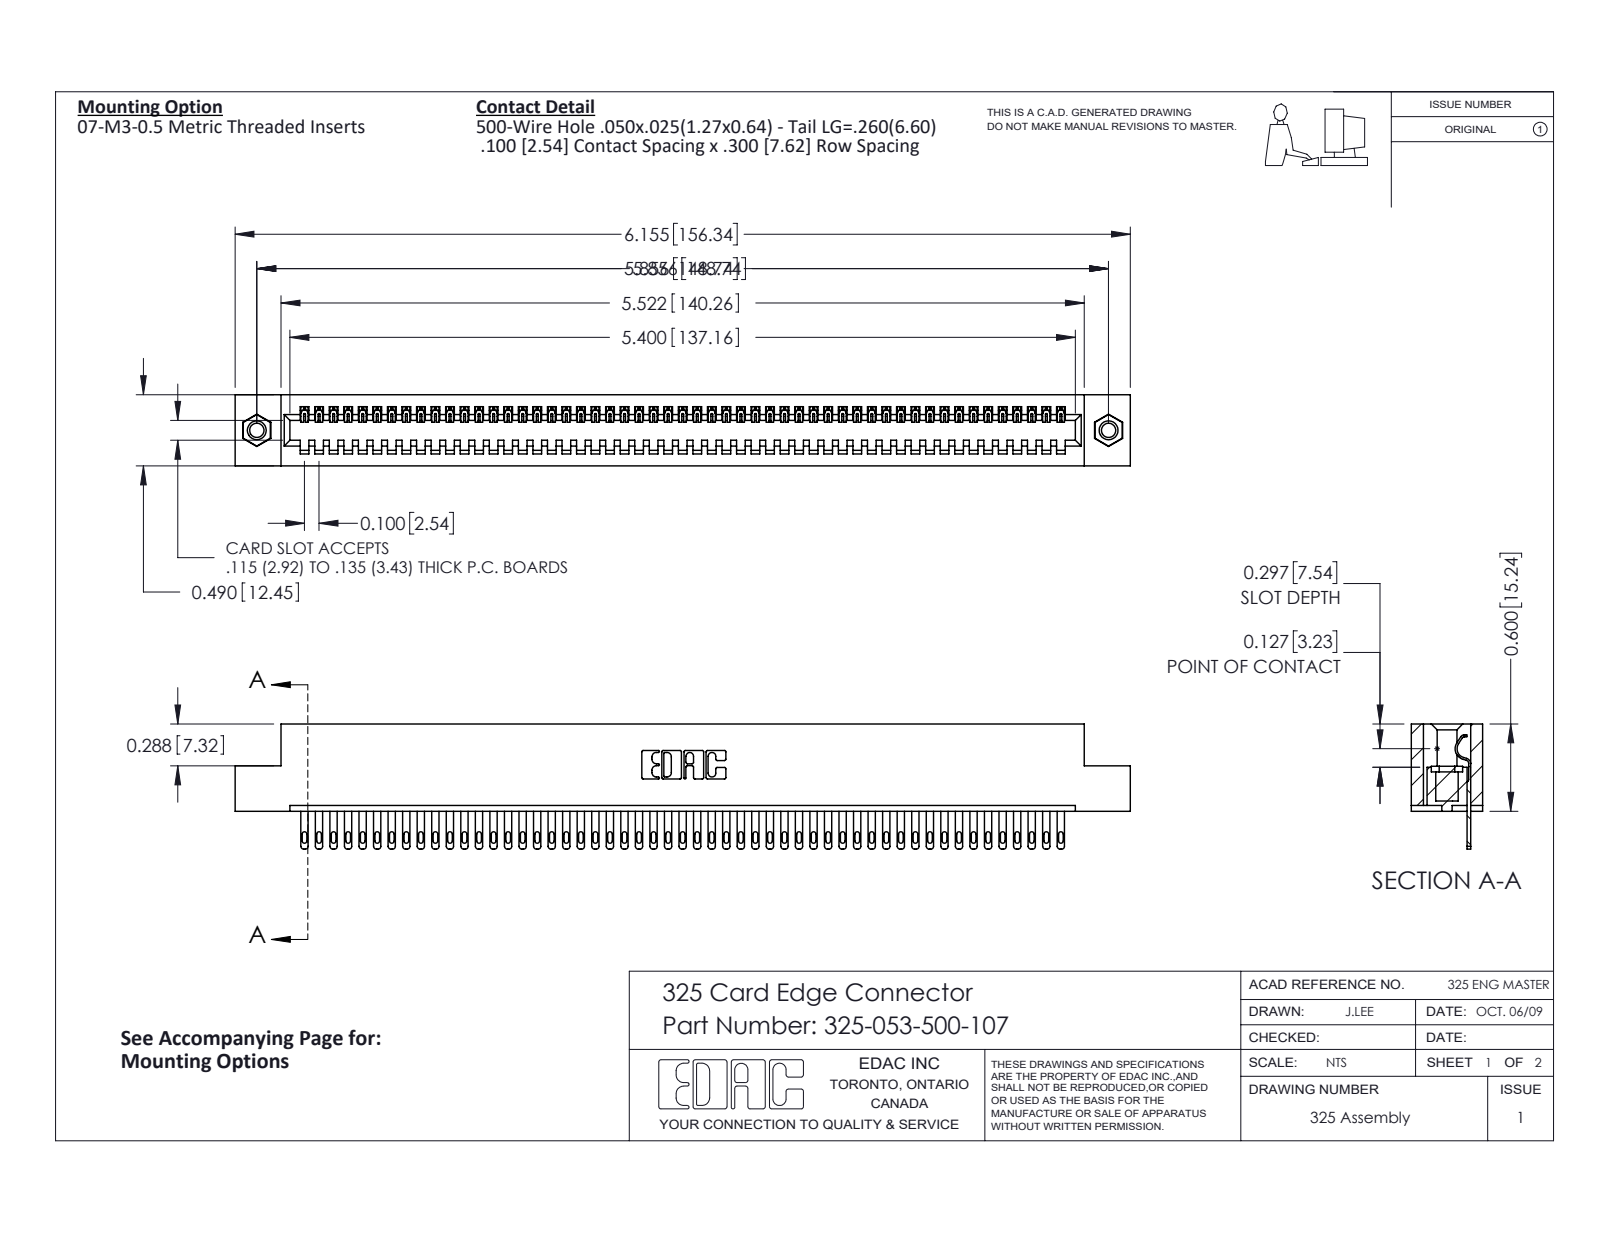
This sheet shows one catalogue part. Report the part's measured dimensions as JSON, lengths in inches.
{"part_name": "325 Part_TI; 325-292-001_325-293-100; 345-250-001_345-250-005-103; 325-053-500-107", "step_written_by": "SolidWorks 2016 (CONFIG_CONTROL_DESIGN)", "units": "inches", "bodies": {"solids": 56, "faces": 3036, "planar": 2010, "cylindrical": 1010, "other": 16}, "overall_size": [6.155, 0.86, 0.49], "volume_in3": 1.218, "surface_area_in2": 34.31, "round_holes": [[0.098, 2], [0.125, 2], [0.16, 2]], "round_bosses_or_shafts": [[0.155, 2]], "partial_cylinders_radius": [[0.006, 106], [0.016, 106], [0.02, 106], [0.01, 22], [0.007, 6], [0.031, 6], [0.026, 3], [0.014, 1]], "face_to_face_distances": [0.083, 0.407, 0.49, 0.3, 0.107, 0.383, 0.025, 0.325, 0.263, 0.56], "hole_center_spacings": [5.856]}
